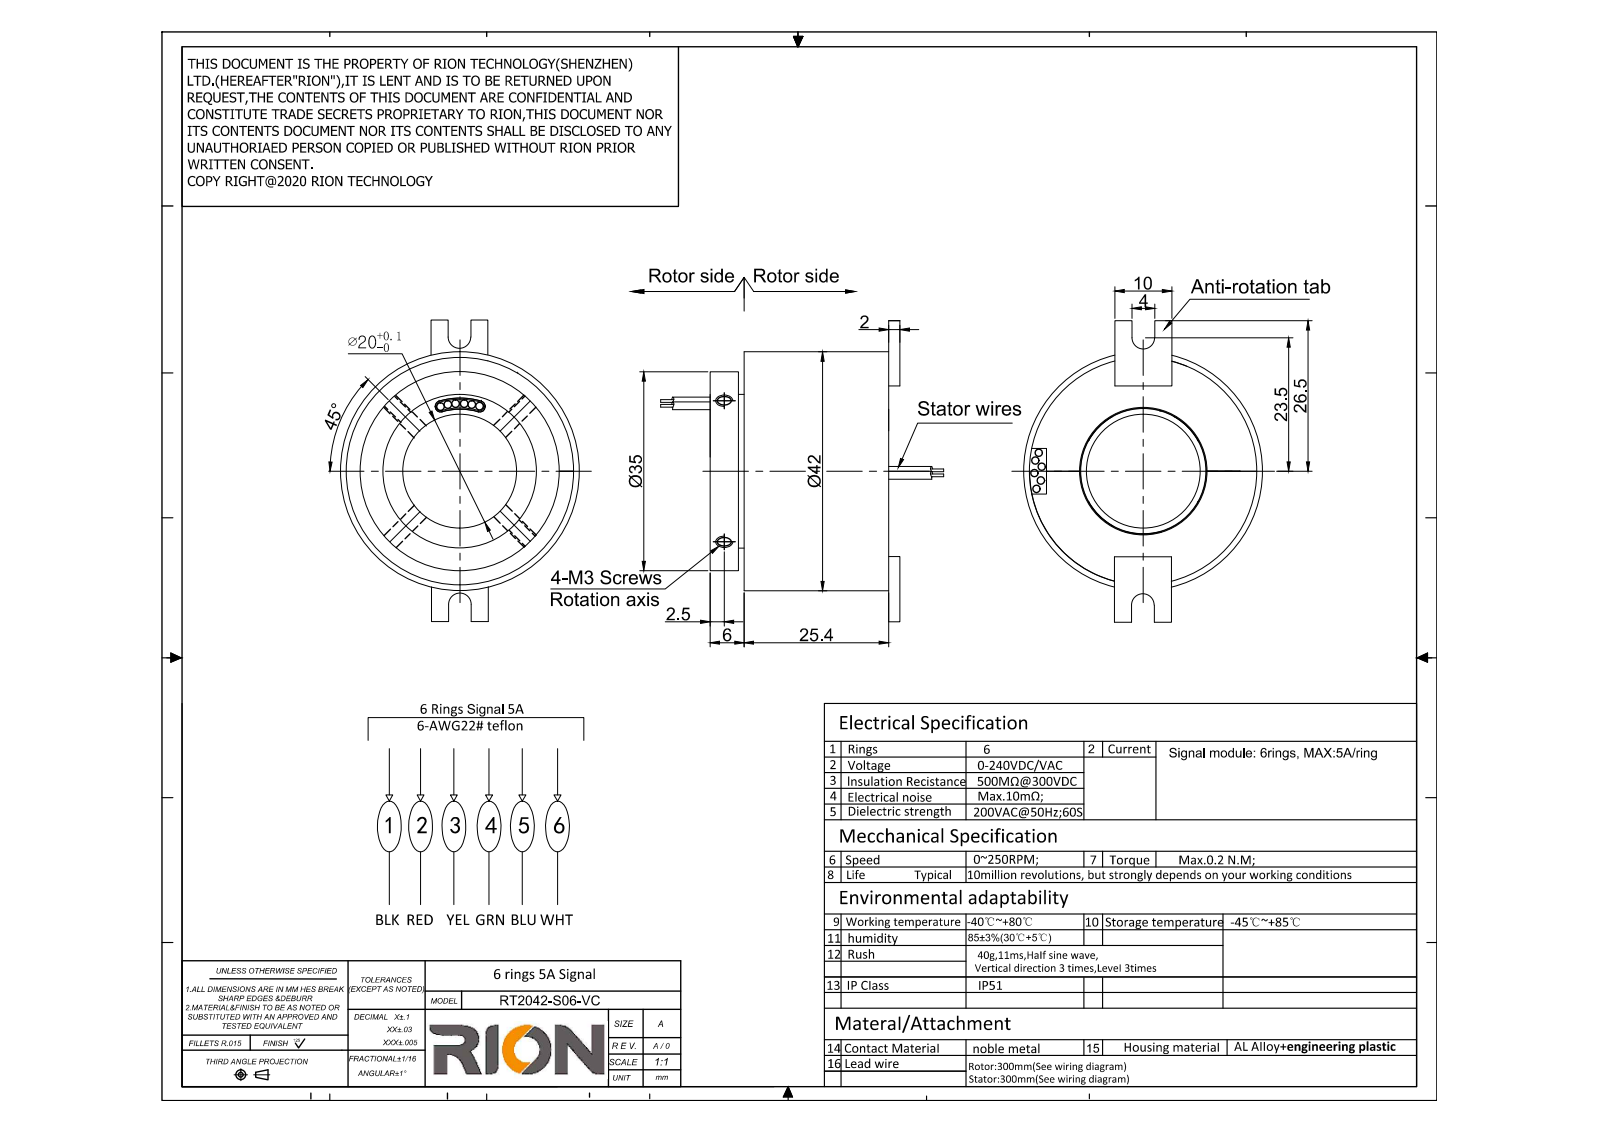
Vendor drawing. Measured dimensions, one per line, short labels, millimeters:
name: MT2042-S06
written by: SolidWorks 2014 (CONFIG_CONTROL_DESIGN)
unit: mm
bodies: 1 solid, 115 faces (48 planar, 67 cylindrical, 0 other)
size: 53 × 49.9 × 42
volume: 30 999 mm³; area: 11 727 mm²
holes: 4× ⌀2.5, 1× ⌀20, 1× ⌀22.2, 1× ⌀40
bosses: 12× ⌀1.3, 1× ⌀42, 1× ⌀39.9, 1× ⌀39.8, 1× ⌀35, 1× ⌀27, 1× ⌀22
rounds: 2× R0.75, 2× R0.75, 2× R2, 1× R11.25, 1× R11.25, 1× R12.75, 1× R12.75
face distances: 25.4, 6, 31.4, 1, 5, 26.4, 2, 33.4, 28.4, 27.4
